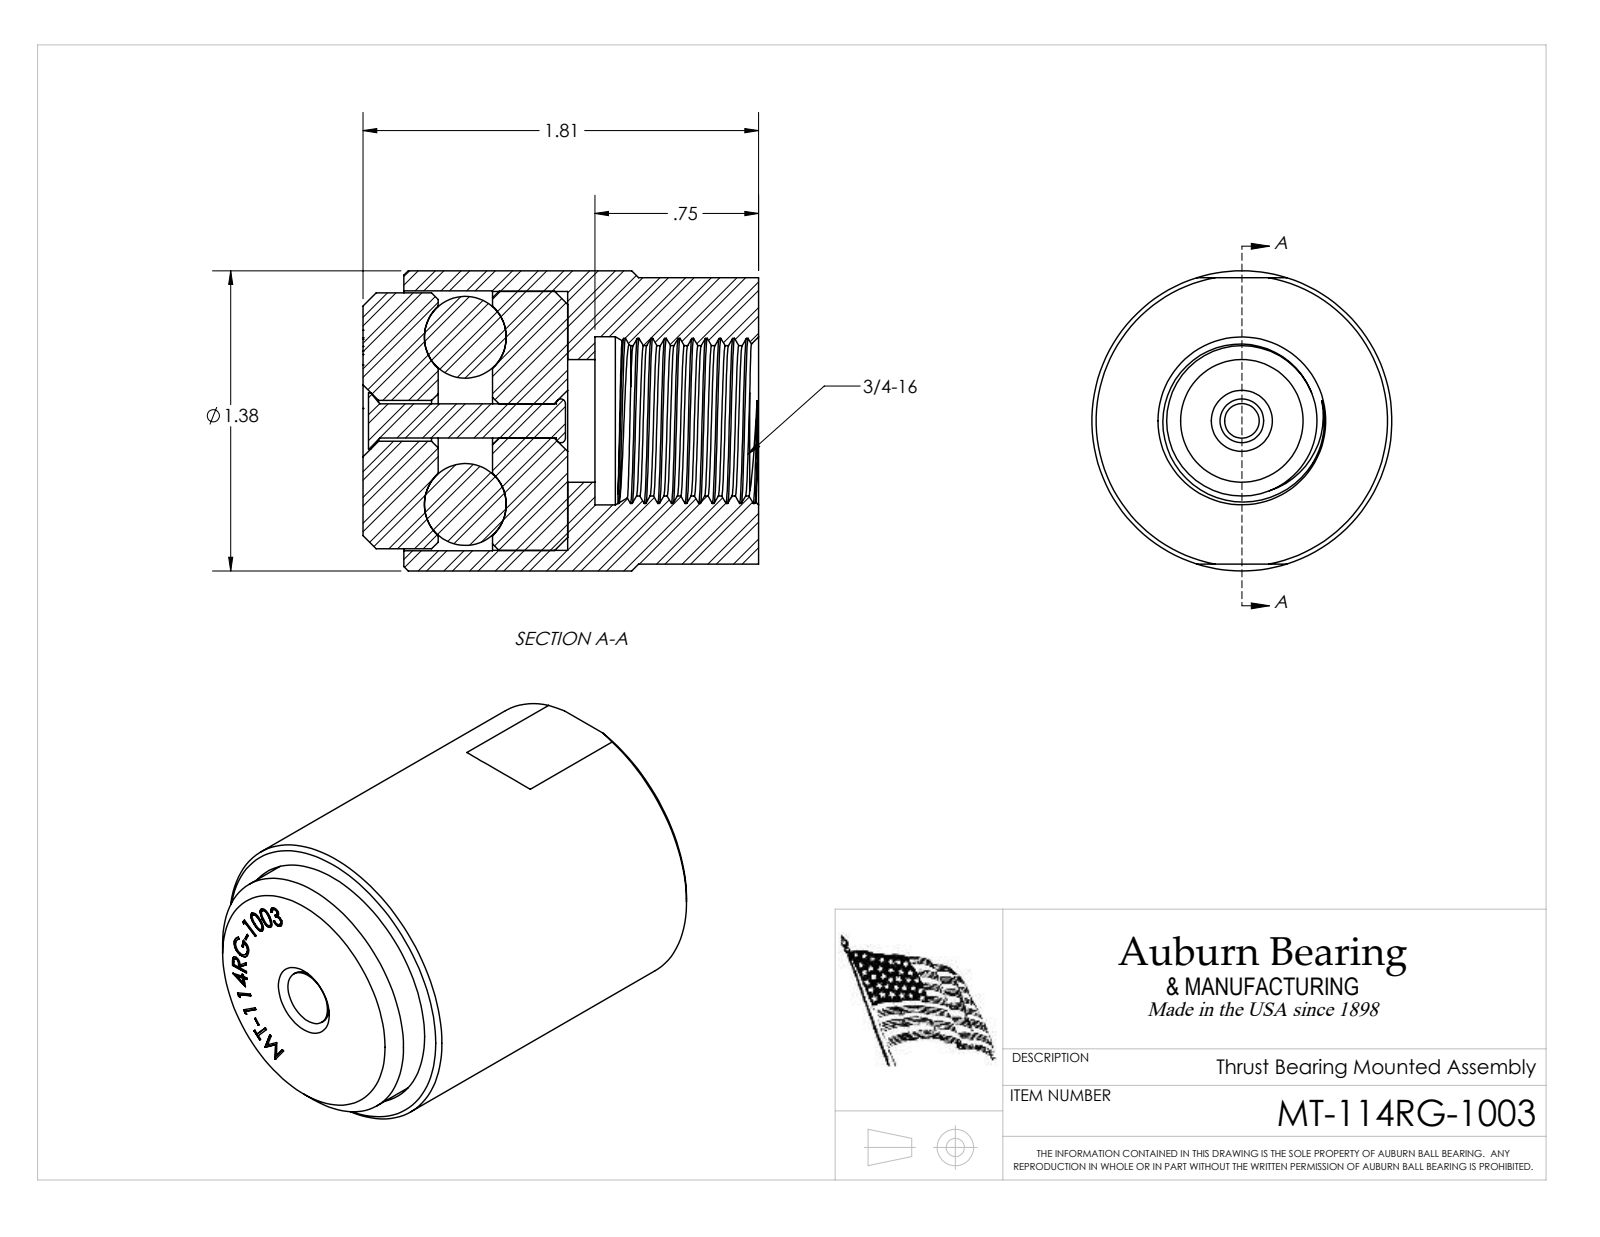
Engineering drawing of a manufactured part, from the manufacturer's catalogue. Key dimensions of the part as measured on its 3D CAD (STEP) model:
Part name (STEP PRODUCT): MT-114RG-1003
STEP written by: SolidWorks 2020 (CONFIG_CONTROL_DESIGN)
Units: inches
Bodies: 10 solids, 250 faces (113 planar, 41 cylindrical, 96 other)
Overall size (bounding box): 1.813 × 1.375 × 1.375
Volume: 2.067 in³ · Surface area: 25.14 in²
Round holes (diameter × count): ⌀0.156 ×1, ⌀0.187 ×1, ⌀0.562 ×1, ⌀0.689 ×1, ⌀0.77 ×1, ⌀1.187 ×1, ⌀1.19 ×1
Round bosses / shafts (diameter × count): ⌀1.375 ×1, ⌀1.187 ×1, ⌀1.172 ×1, ⌀0.256 ×1
Main face-to-face distances: 0.875, 0.938, 1.813, 0.344, 0.594, 0.187, 0.751, 1.626, 0.407, 1.219
